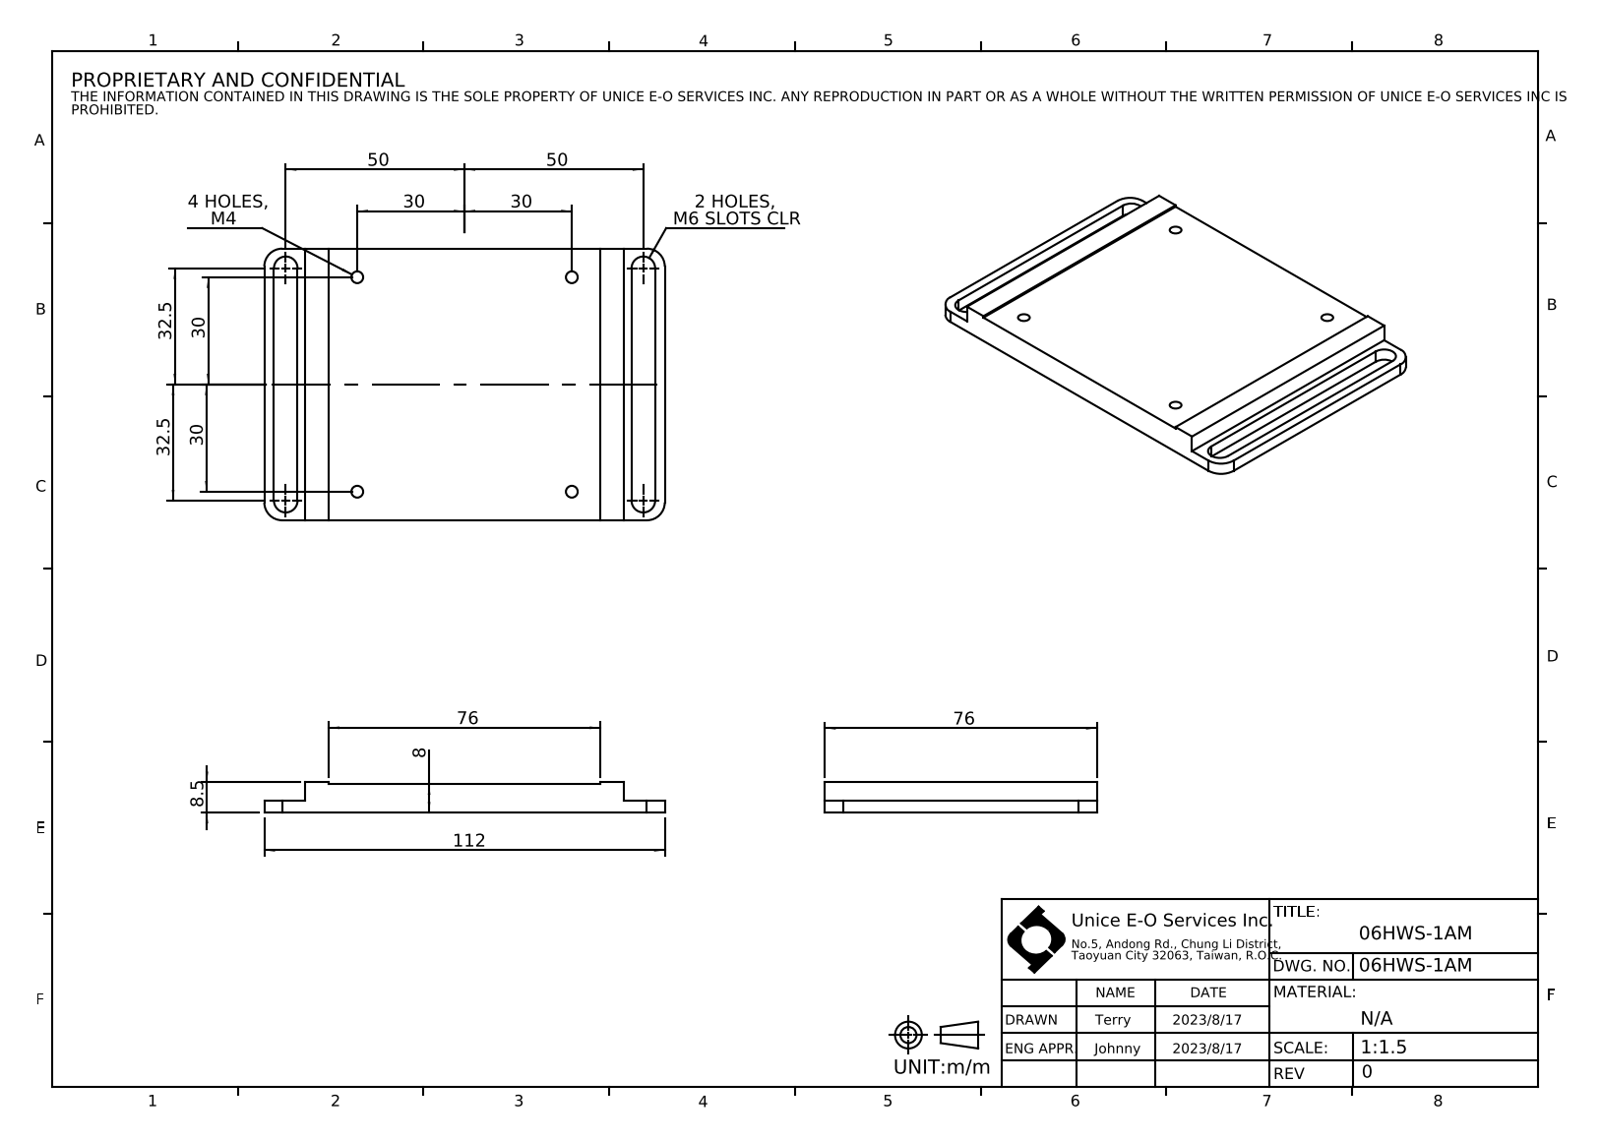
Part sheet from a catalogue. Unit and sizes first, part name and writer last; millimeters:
Units: millimetres
Overall size (bounding box): 112 × 76 × 8.5
Round holes (diameter × count): ⌀3.3 ×4
Partial cylindrical surfaces — rounded edges, fillets, slot ends (radius × count): R3.3 ×4, R5 ×4
Main face-to-face distances: 8, 8.5, 0.5, 76, 3.5, 4.5, 5, 11.5, 100.5, 2.7
Hole centre spacings: 60, 84.85
Volume: 57 133 mm³ · Surface area: 19 383 mm²
Bodies: 1 solid, 30 faces (18 planar, 12 cylindrical, 0 other)
Part name (STEP PRODUCT): 06HWS-1AM
STEP written by: SolidWorks 2022 (CONFIG_CONTROL_DESIGN)
